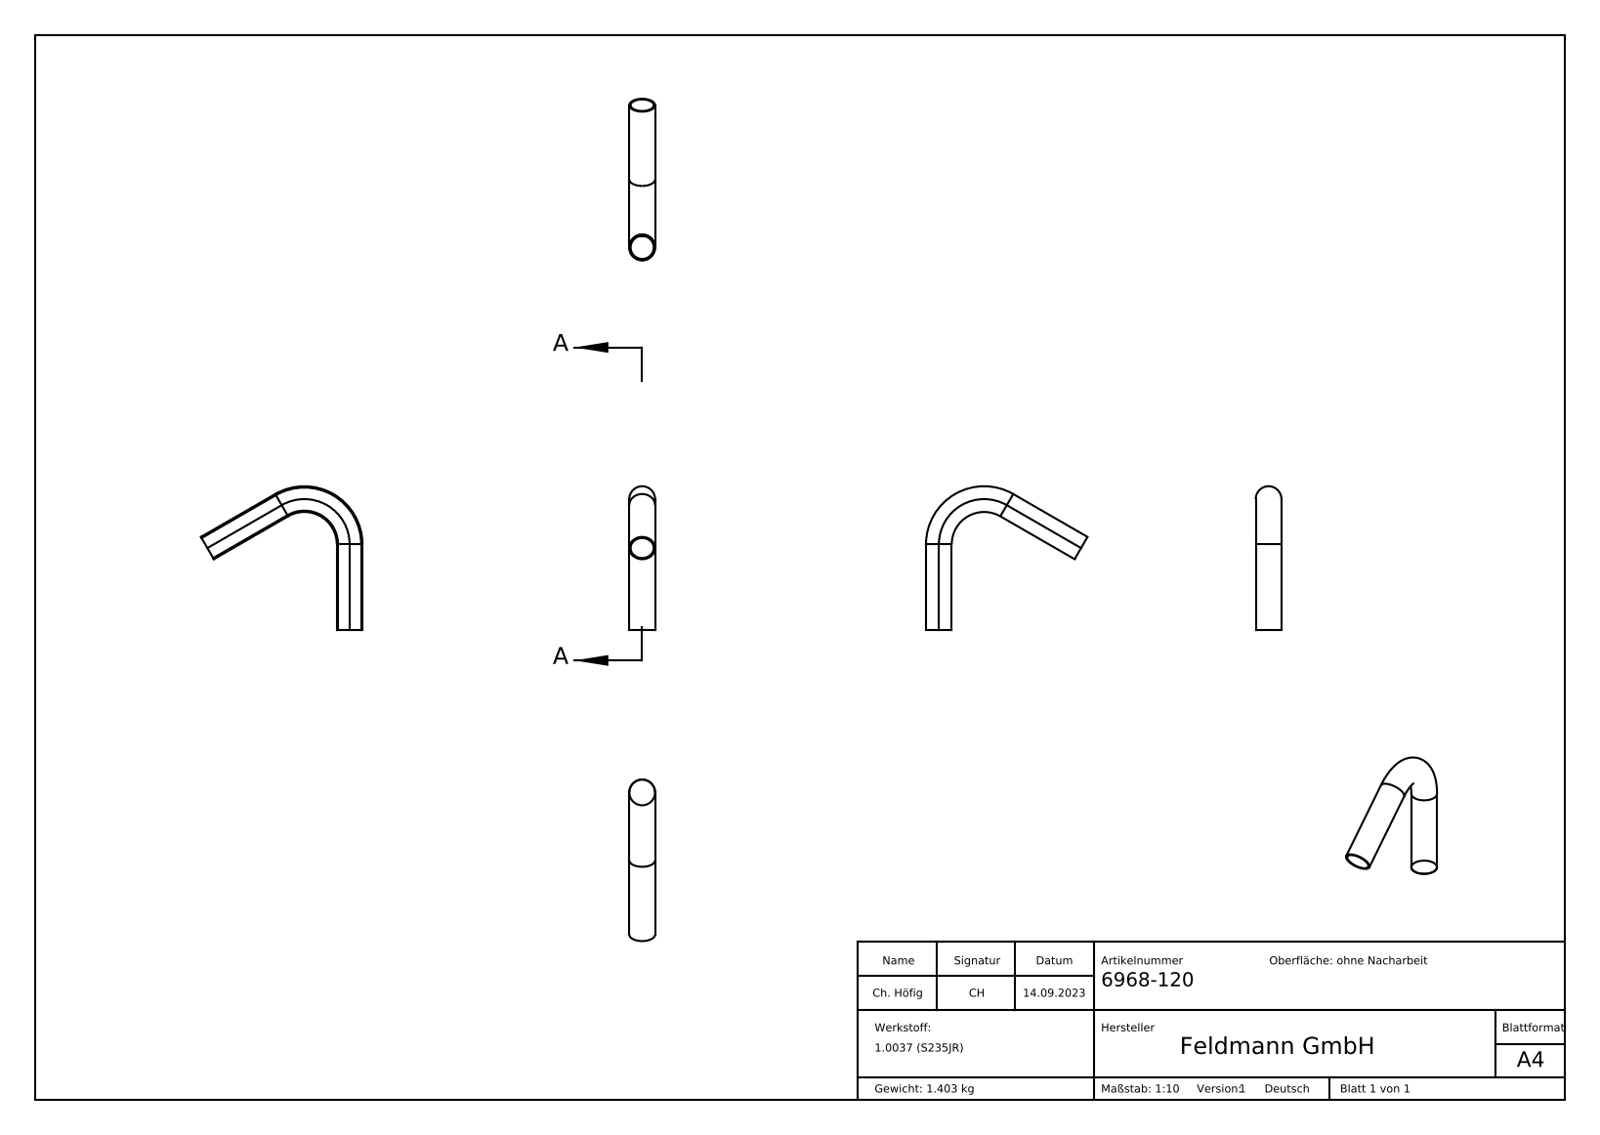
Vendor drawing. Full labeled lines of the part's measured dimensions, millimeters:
Part name (STEP PRODUCT): 6968-120
STEP written by: SolidWorks 2018 (CONFIG_CONTROL_DESIGN)
Units: millimetres
Bodies: 1 solid, 219 faces (106 planar, 4 cylindrical, 109 other)
Overall size (bounding box): 303.14 × 270.14 × 48.3
Volume: 179 856 mm³ · Surface area: 144 608 mm²
Round holes (diameter × count): ⌀43.3 ×2
Round bosses / shafts (diameter × count): ⌀48.3 ×2
Main face-to-face distances: 0.5, 0.55, 0.53, 0.34, 0.31, 0.45, 0.58, 0.39, 0.48, 0.36
